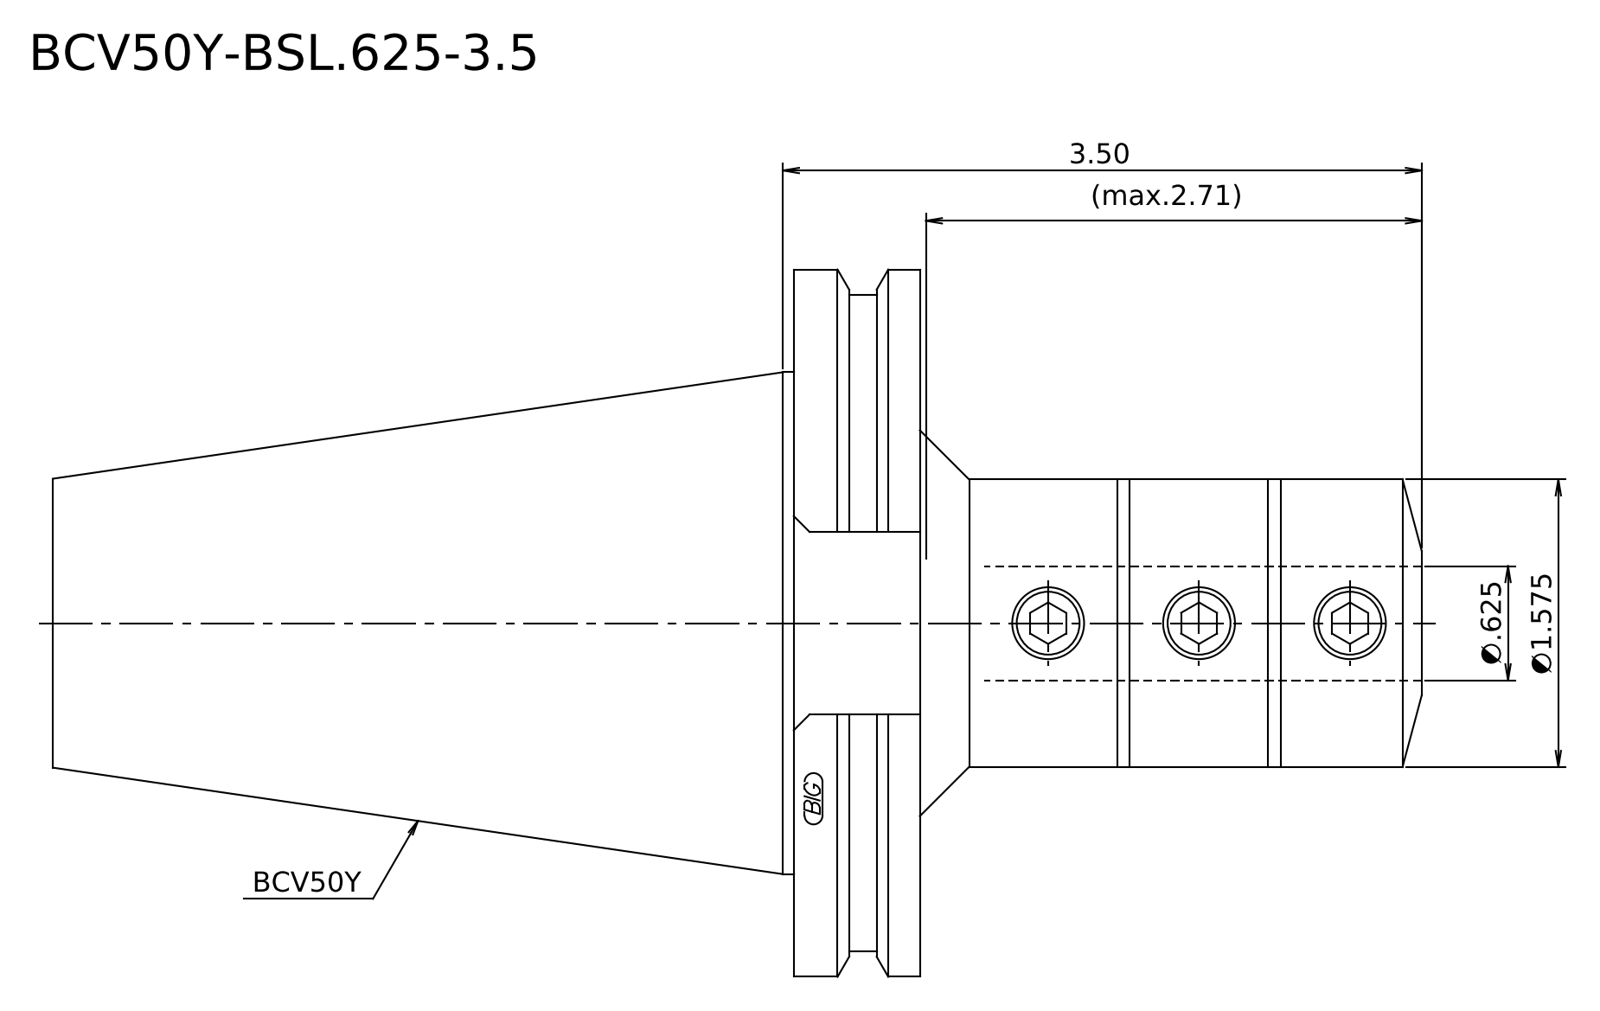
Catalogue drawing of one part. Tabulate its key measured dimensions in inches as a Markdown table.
| quantity | value |
| --- | --- |
| STEP written by | Kubotek KeyCreator 2011 V10.0.2 (22737) (automotive_design) |
| units | inches |
| bodies | 1 solid, 16 faces (6 planar, 5 cylindrical, 5 other) |
| overall size | 7.5 × 3.875 × 3.875 |
| volume | 28.74 in³ |
| surface area | 70.52 in² |
| round bosses / shafts (diameter × count) | 3.875 × 1, 3.594 × 1, 2.75 × 1, 1.575 × 1 |
| main face-to-face distances | 0.691, 4.75, 4.059, 2.75, 3.441, 7.5, 2.987, 0.237, 0.454, 4.513 |
